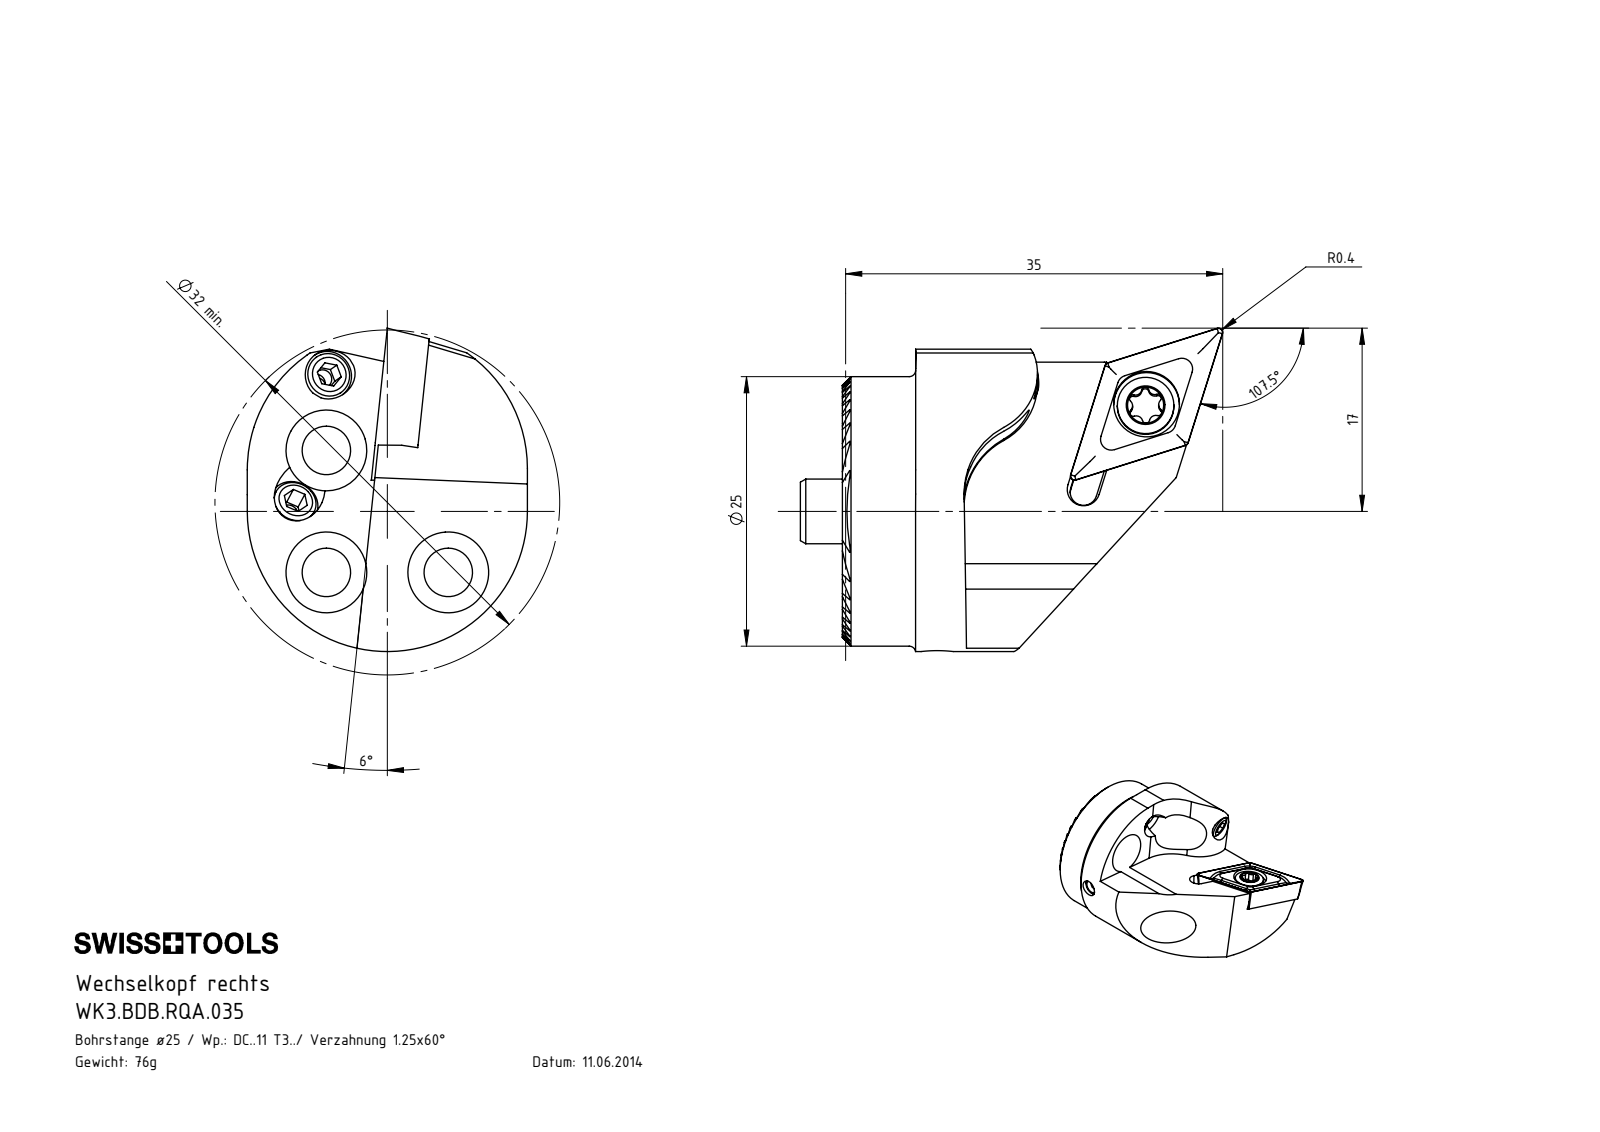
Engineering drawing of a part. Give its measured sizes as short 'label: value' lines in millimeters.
name: WK3.BDB.RQA.035; WK3-BDB.RQA.035_A; DCMT11T304; KVT_MB_600_030 (+3 more)
written by: SolidWorks 2017 (AUTOMOTIVE_DESIGN)
unit: mm
bodies: 12 solids, 527 faces (180 planar, 175 cylindrical, 172 other)
size: 39.2 × 30.01 × 26
volume: 9 445 mm³; area: 6 452 mm²
holes: 5× ⌀4.5, 3× ⌀2.38, 3× ⌀2.5, 3× ⌀3.3, 3× ⌀7.5, 2× ⌀1.7, 2× ⌀3, 1× ⌀4.2, 1× ⌀4.4, 1× ⌀6, 1× ⌀6.1
bosses: 3× ⌀4, 3× ⌀3, 1× ⌀25, 1× ⌀5.25
rounds: 20× R0.12, 6× R0.34, 6× R0.59, 3× R13, 2× R7, 1× R1.25, 1× R6
face distances: 4.33, 1.08, 3.25, 5.41, 8.66, 7.58, 2.16, 2.17, 3.66, 9.74
hole spacings: 8, 11.32, 16.01
